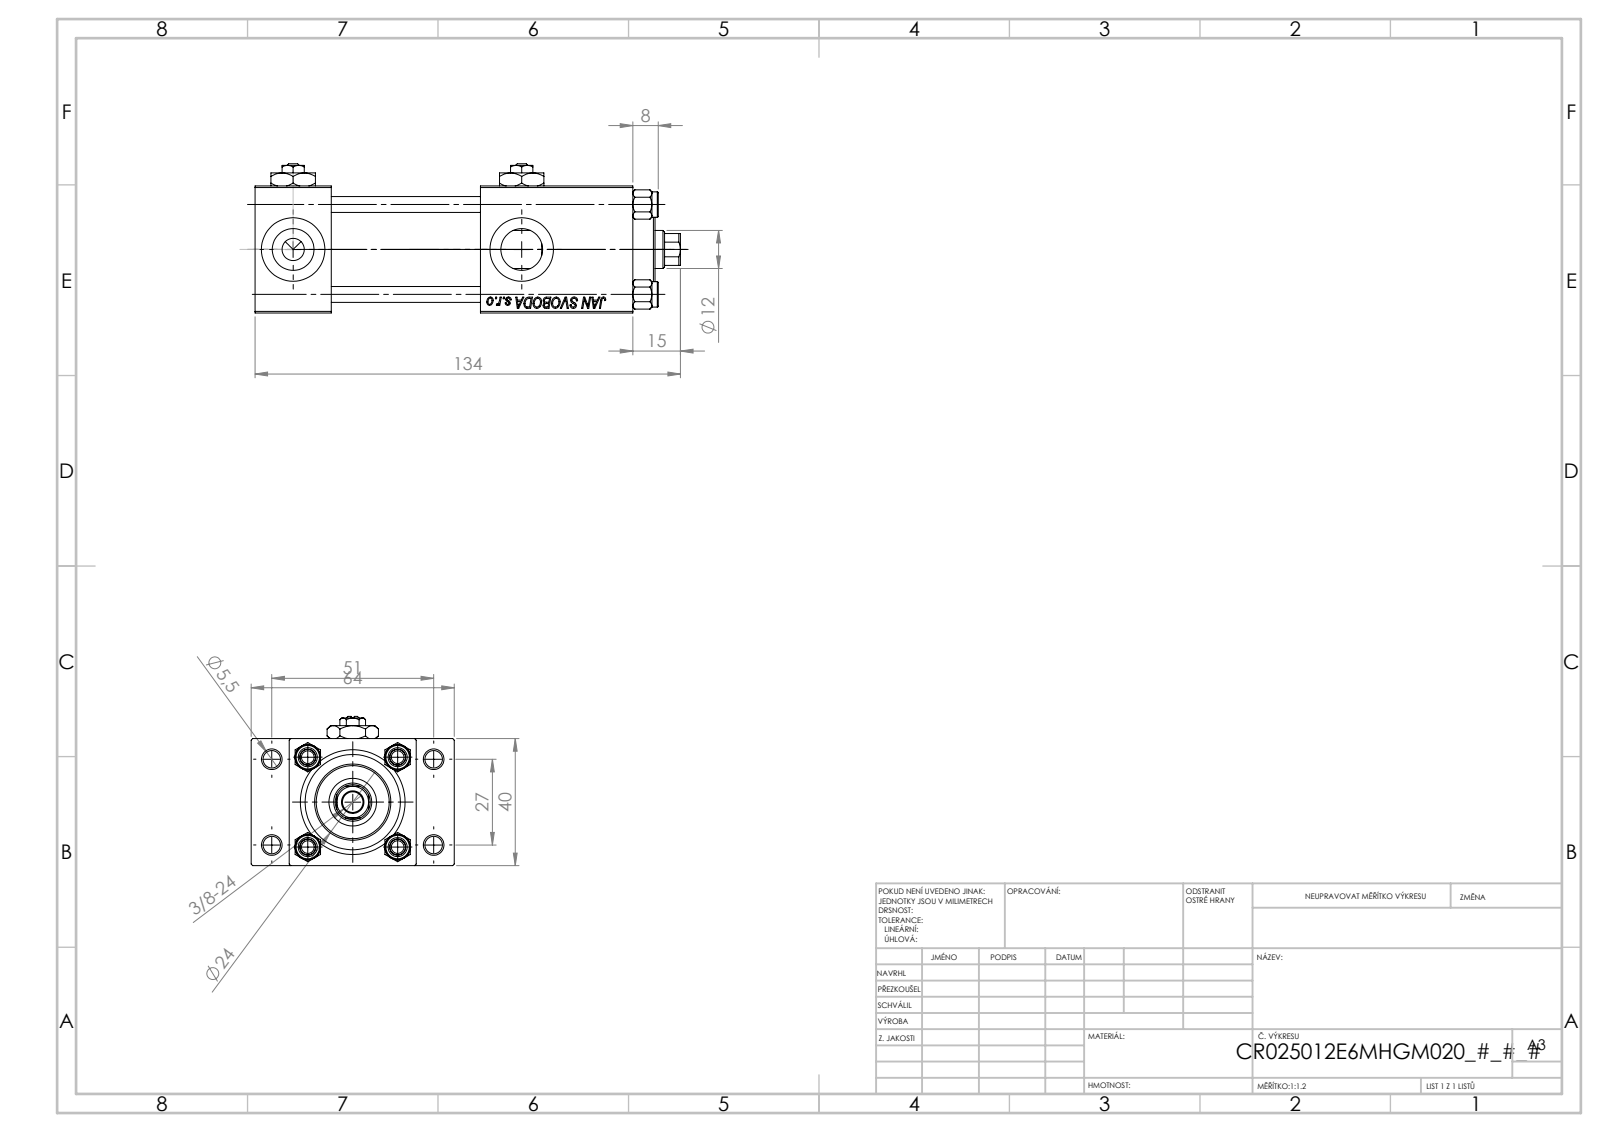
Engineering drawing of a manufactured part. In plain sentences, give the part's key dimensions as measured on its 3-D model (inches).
The part is named "NUT_M5_E; Zatka_pro_OIL_PORT; V215_VC_A; V215CR_VCP_E (+2 more)". Its 3-D file was written by "SolidWorks 2019 (CONFIG_CONTROL_DESIGN)". It is 13 solids with 1235 faces: 544 planar, 97 cylindrical and 594 other. Overall it measures 5.276 by 2.52 by 1.85 inches. Its volume is 9.874 cubic inches and its surface area 99.5 square inches. Round holes: 5 of diameter 0.787, 4 of diameter 0.197, 4 of diameter 0.217, 4 of diameter 0.518, 3 of diameter 0.276, 1 of diameter 0.256, 1 of diameter 0.472, 1 of diameter 0.591, 1 of diameter 0.984, 1 of diameter 1.181. Round bosses or shafts: 4 of diameter 0.315, 1 of diameter 1.22, 1 of diameter 0.945. Partial cylindrical surfaces (rounded edges, fillets, slot ends): 1 of radius 0.217. The main face-to-face distances are 1.575, 0.945, 0.472, 2.047, 4.685, 3.74, 3.555, 2.61, 1.13, 1.85. The hole center spacings are 0.448, 0.788, 1.114, 1.136, 1.177, 1.561, 1.903, 1.063.
